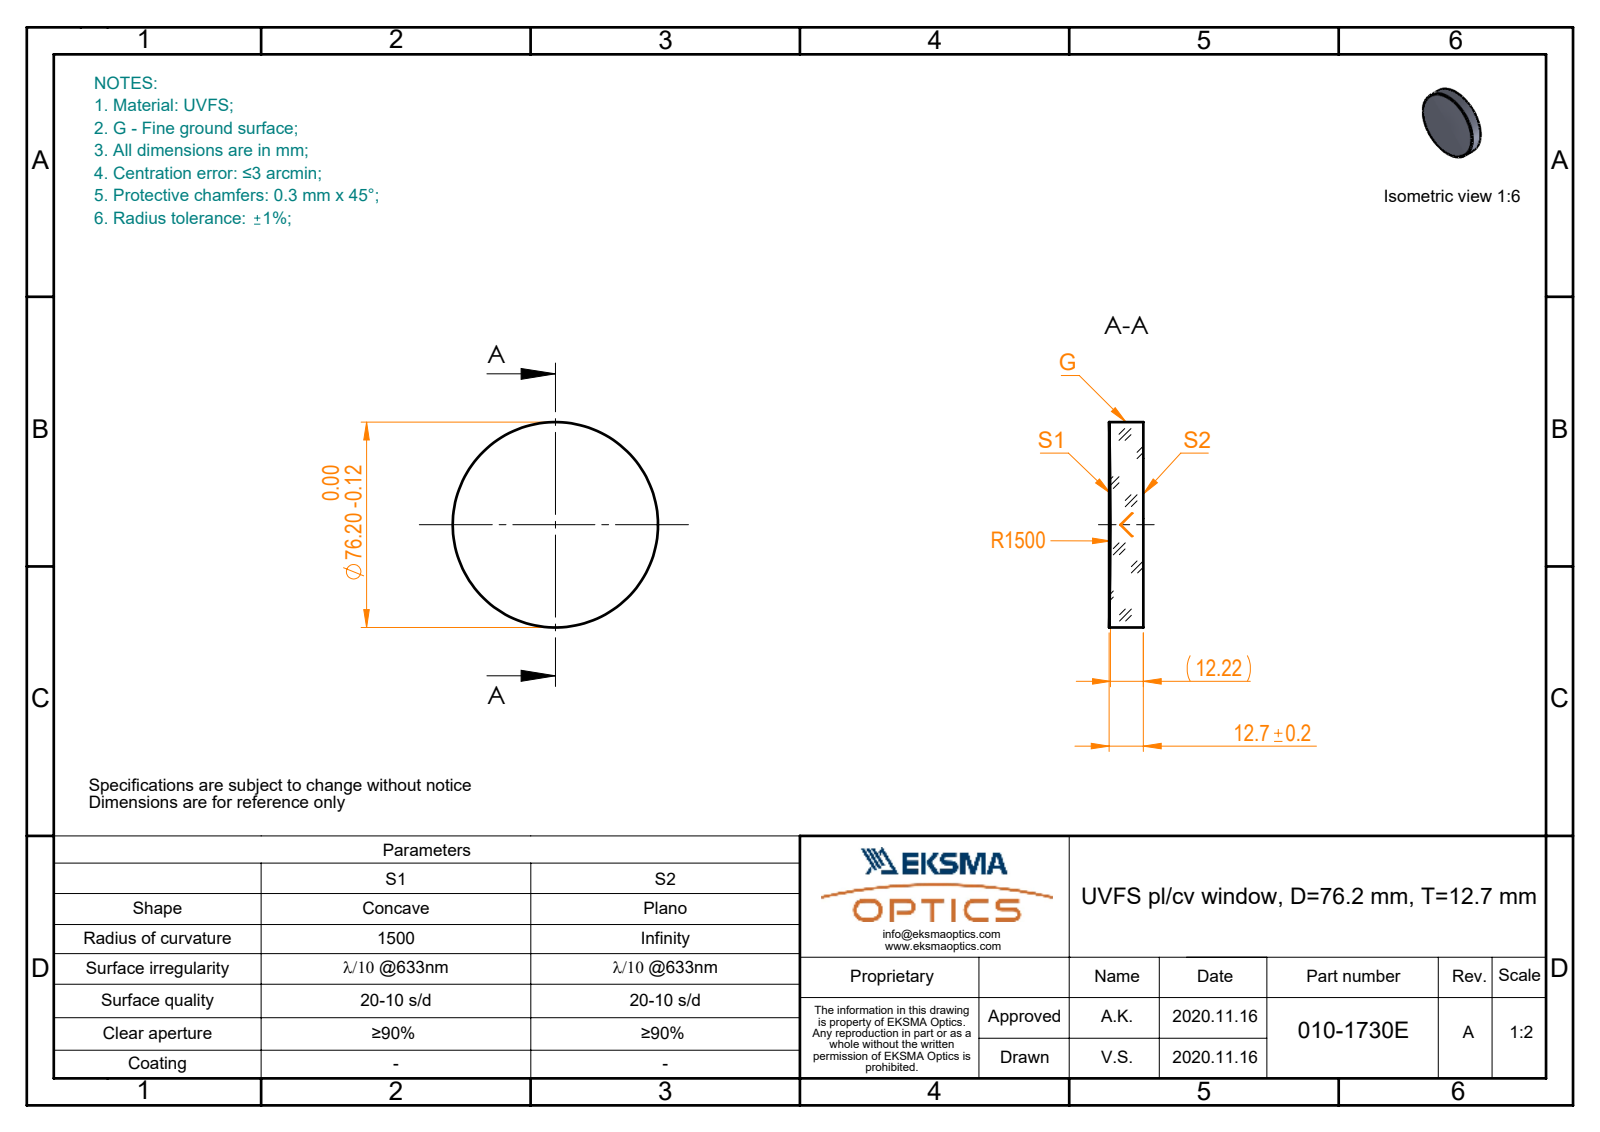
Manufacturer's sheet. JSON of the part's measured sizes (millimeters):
{"part_name": "010-1730E_UVFS_PCV_window", "step_written_by": "SolidWorks 2019 (CONFIG_CONTROL_DESIGN)", "units": "millimeters", "bodies": {"solids": 1, "faces": 5, "planar": 1, "cylindrical": 2, "other": 2}, "overall_size": [76.2, 76.2, 12.7], "volume_mm3": 56813, "surface_area_mm2": 12162, "round_bosses_or_shafts": [[76.2, 1]]}
